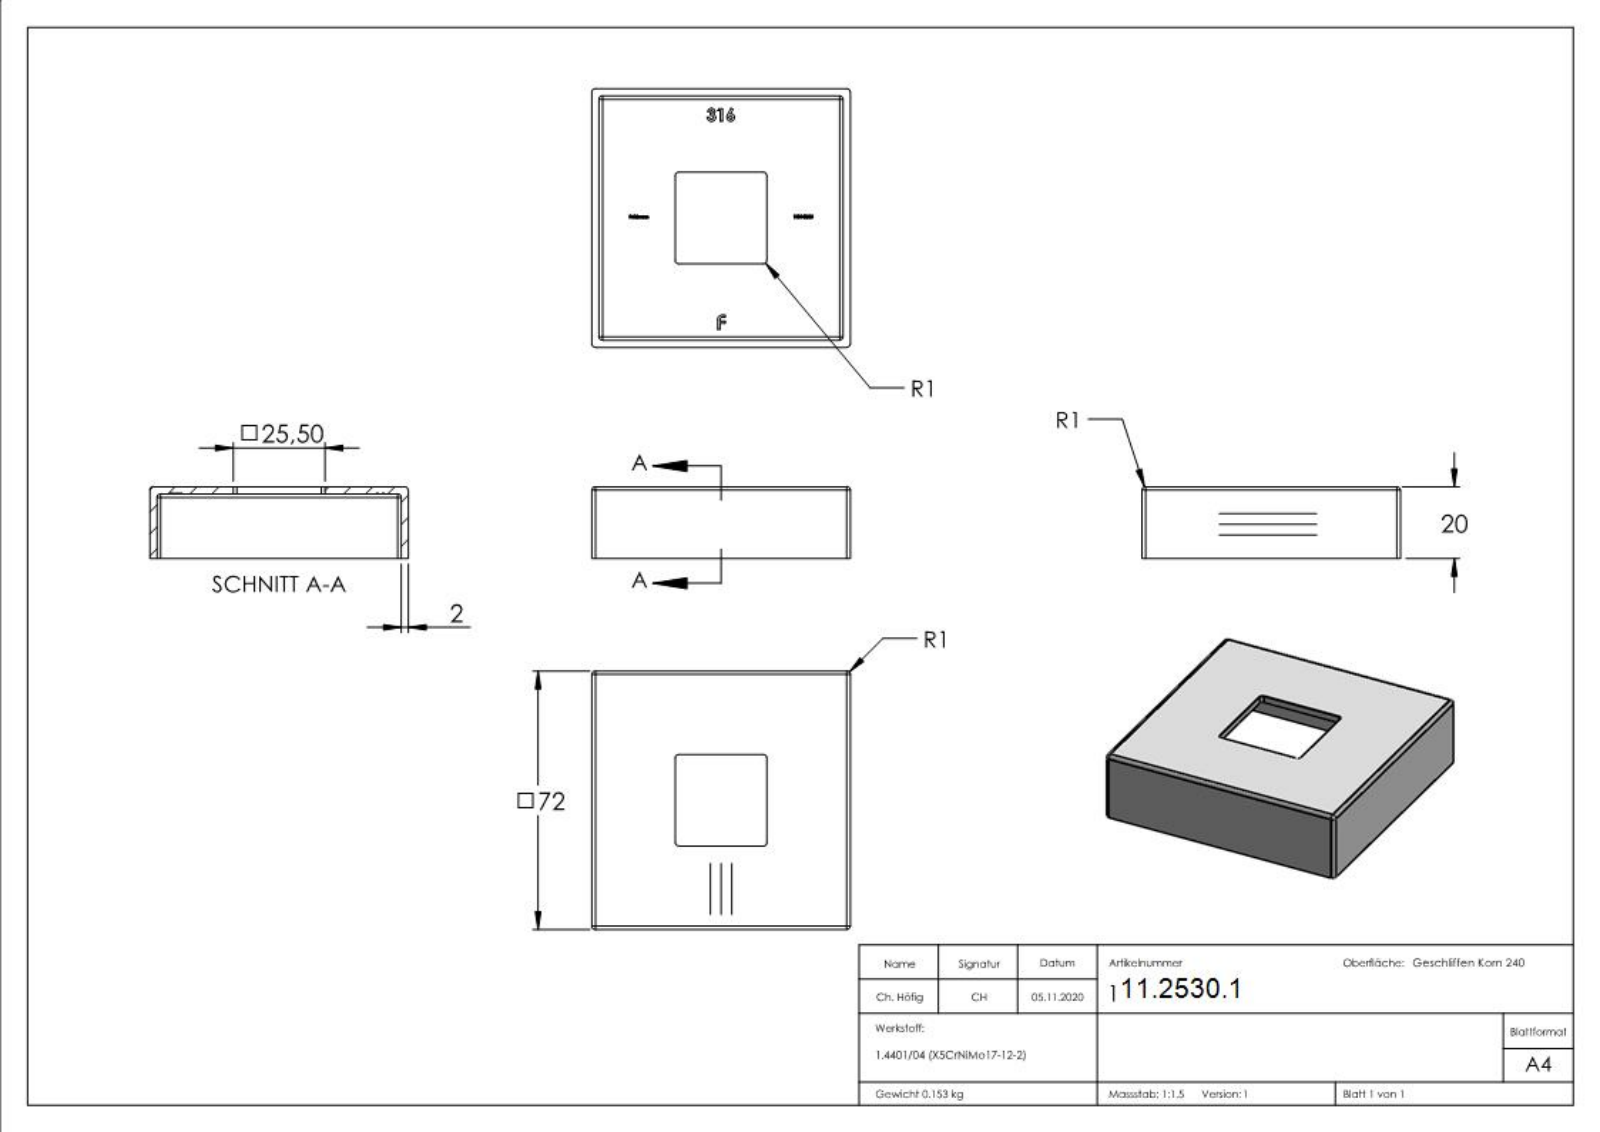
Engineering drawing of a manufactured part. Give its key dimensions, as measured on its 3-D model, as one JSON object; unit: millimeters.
{"part_name": "100042525", "step_written_by": "SolidWorks 2018 (CONFIG_CONTROL_DESIGN)", "units": "millimeters", "bodies": {"solids": 1, "faces": 317, "planar": 163, "cylindrical": 20, "other": 134}, "overall_size": [72, 72, 20], "volume_mm3": 19142, "surface_area_mm2": 19630, "partial_cylinders_radius": [[1, 20]], "face_to_face_distances": [2, 70, 72, 68, 20, 18, 23.25, 48.75, 21.25, 46.75]}
